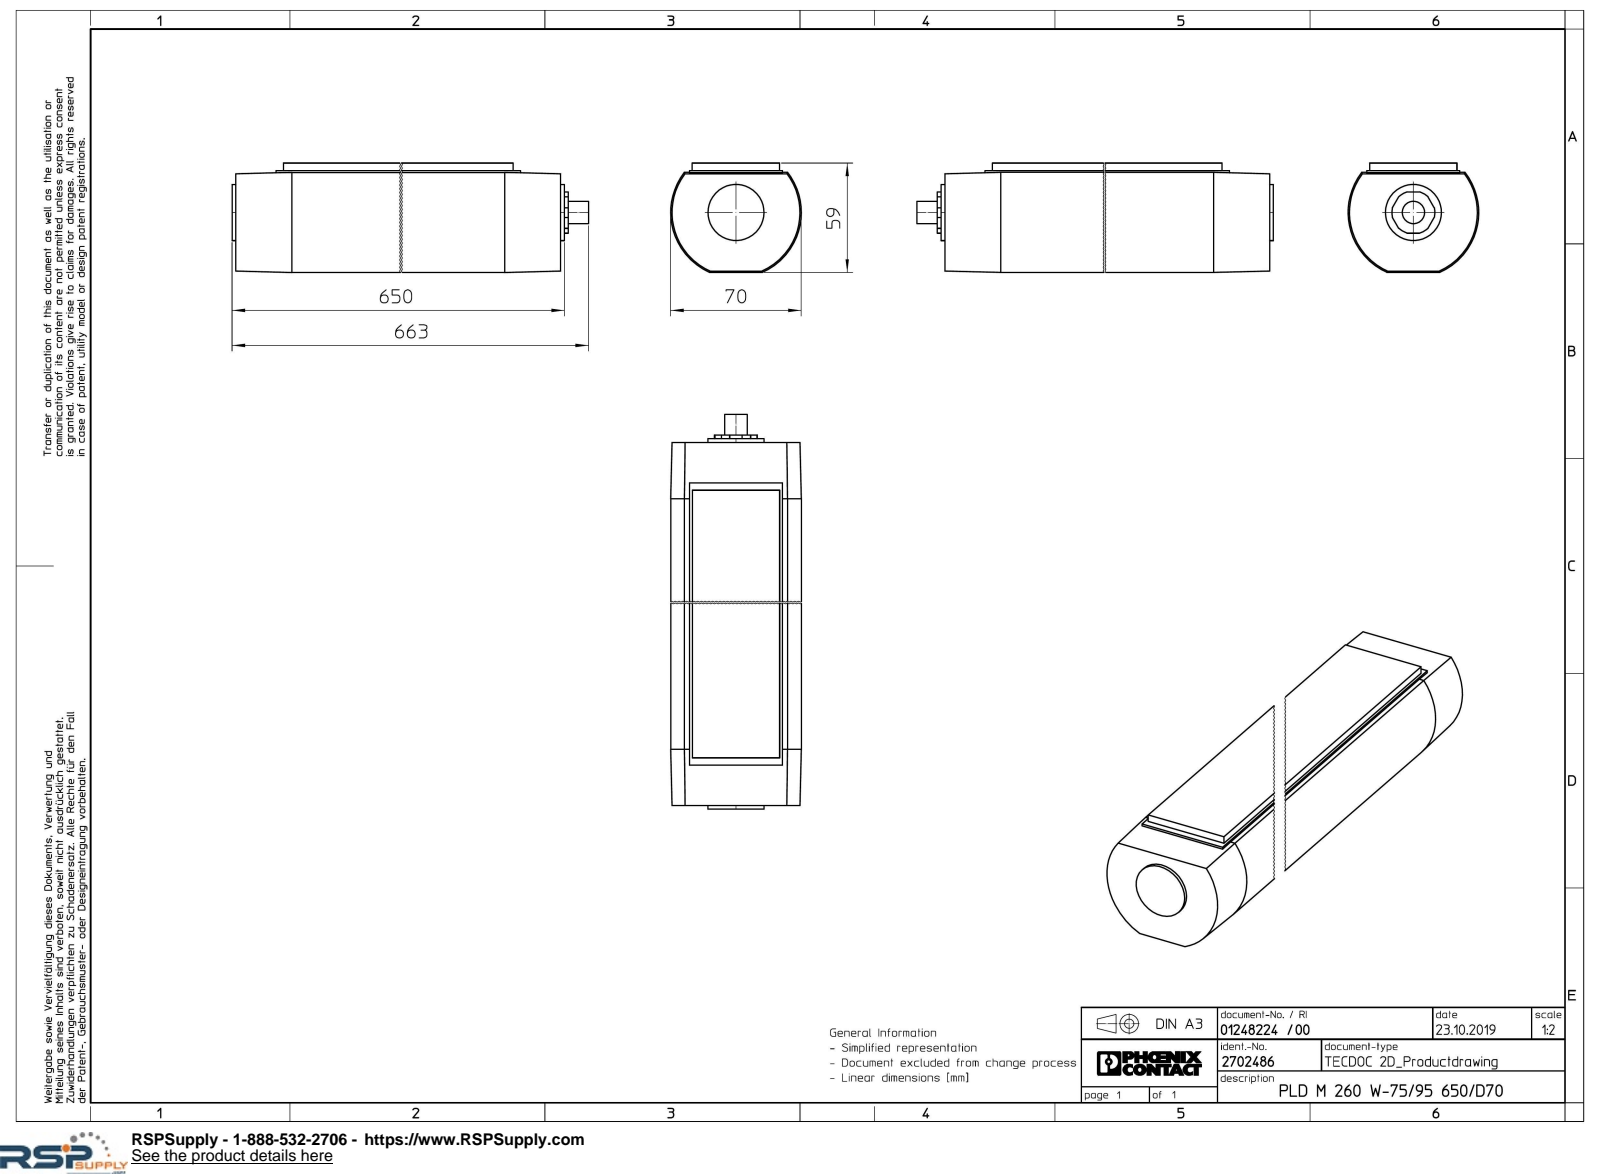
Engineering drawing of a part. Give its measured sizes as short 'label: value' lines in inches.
name: PLD_M_260_W_75_95_650_D70-select
written by: Creo Elements/Direct Modeling 20.1A 29-Sep-2018 (C) Parametric Technology GmbH (AUTOMOTIVE_DESIGN)
unit: in
bodies: 1 solid, 47 faces (29 planar, 14 cylindrical, 4 other)
size: 26.1 × 2.756 × 2.303
volume: 137.6 in³; area: 231.8 in²
bosses: 1× ⌀1.181, 1× ⌀0.472
rounds: 1× R0.453, 1× R1.378
face distances: 2.303, 2.106, 0.197, 0.157, 25.433, 1.843, 2.146, 0.039, 0.079, 0.059
